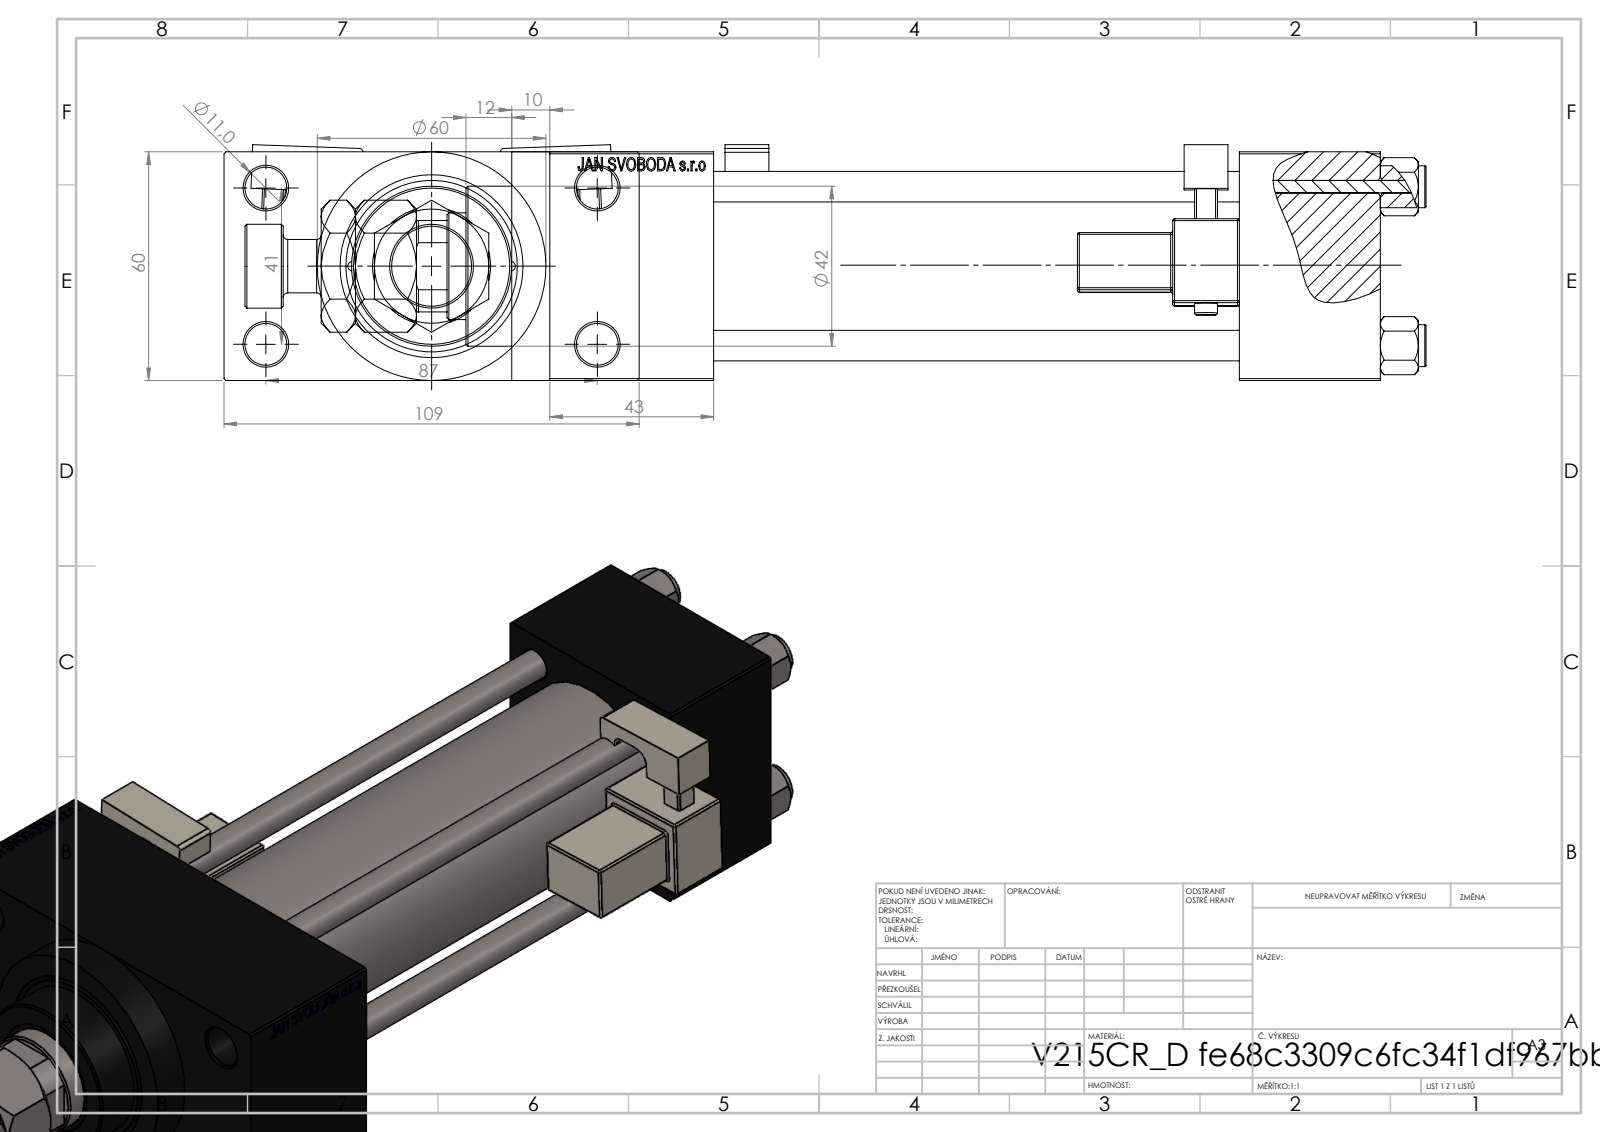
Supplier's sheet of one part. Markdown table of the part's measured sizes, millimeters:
| quantity | value |
| --- | --- |
| part name | V215CR_MSU; V215CR_VCP_D; MFA; V215_VC_A (+3 more) |
| STEP written by | SolidWorks 2019 (CONFIG_CONTROL_DESIGN) |
| units | millimeters |
| bodies | 14 solids, 1320 faces (576 planar, 156 cylindrical, 588 other) |
| overall size | 310 × 109 × 61.9 |
| volume | 691 902 mm³ |
| surface area | 183 446 mm² |
| round holes (diameter × count) | 8 × 4, 11 × 4, 2.5 × 2, 7 × 2, 16.66 × 2, 24 × 2, 18.5 × 1, 28 × 1, 31 × 1, 40 × 1, 45 × 1 |
| round bosses / shafts (diameter × count) | 11 × 4, 6 × 2, 60 × 1, 46 × 1, 42 × 1, 22 × 1, 14 × 1 |
| partial cylindrical surfaces (radius × count) | 0.5 × 48, 1 × 2, 2.5 × 2, 4 × 2, 13.5 × 1 |
| main face-to-face distances | 60, 138, 24.5, 84.5, 37, 175, 218, 181, 43, 109 |
| hole center spacings | 20.85, 22.65, 29.49, 30.62, 41.7, 46.53, 47.15, 48.09 |
